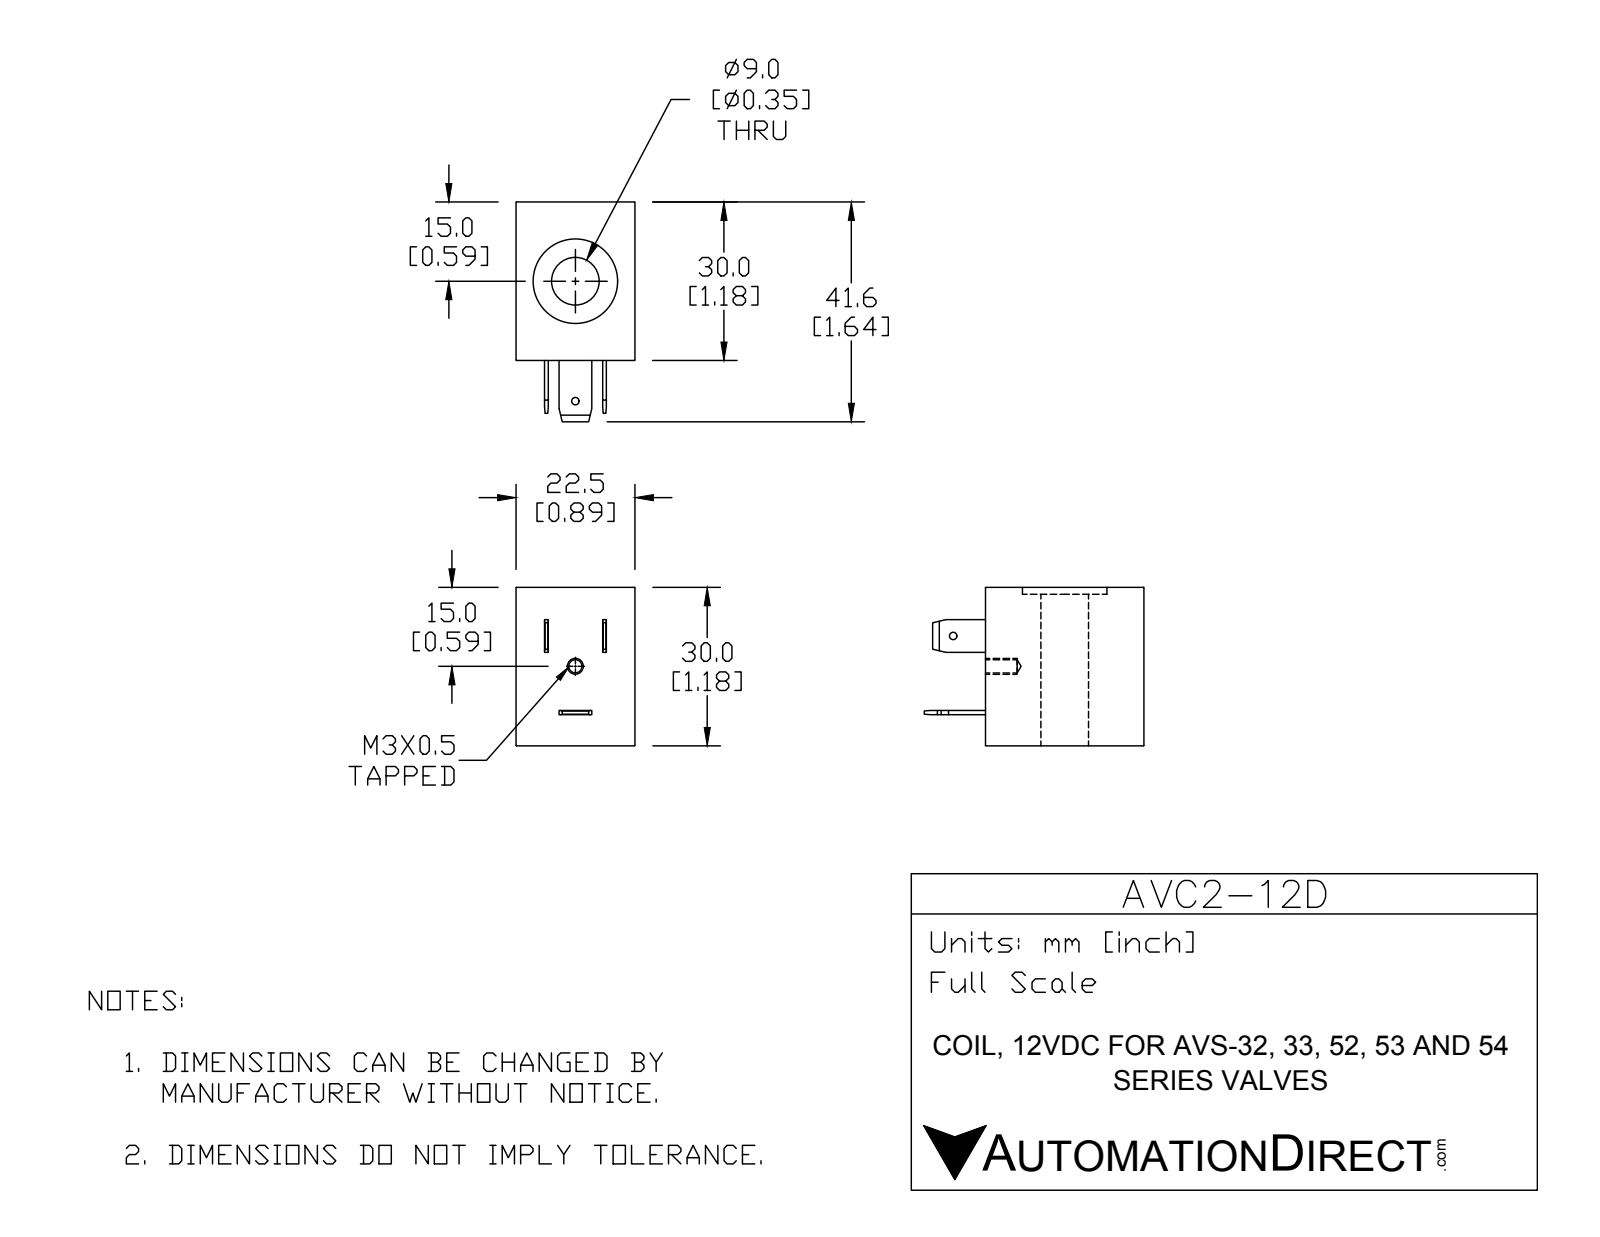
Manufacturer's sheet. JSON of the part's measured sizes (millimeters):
{"part_name": "AVC2-12D", "step_written_by": "SolidWorks 2016 (AUTOMOTIVE_DESIGN)", "units": "millimeters", "bodies": {"solids": 1, "faces": 60, "planar": 34, "cylindrical": 20, "other": 6}, "overall_size": [41.6, 30, 22.5], "volume_mm3": 18267, "surface_area_mm2": 5712, "round_holes": [[1.4, 2], [2.5, 1], [9, 1], [16, 1]], "partial_cylinders_radius": [[0.1, 8]], "face_to_face_distances": [30, 22.5, 28.7, 1.3, 11, 6.1, 16.4, 5.4, 17.1, 0.7], "hole_center_spacings": [22.7]}
